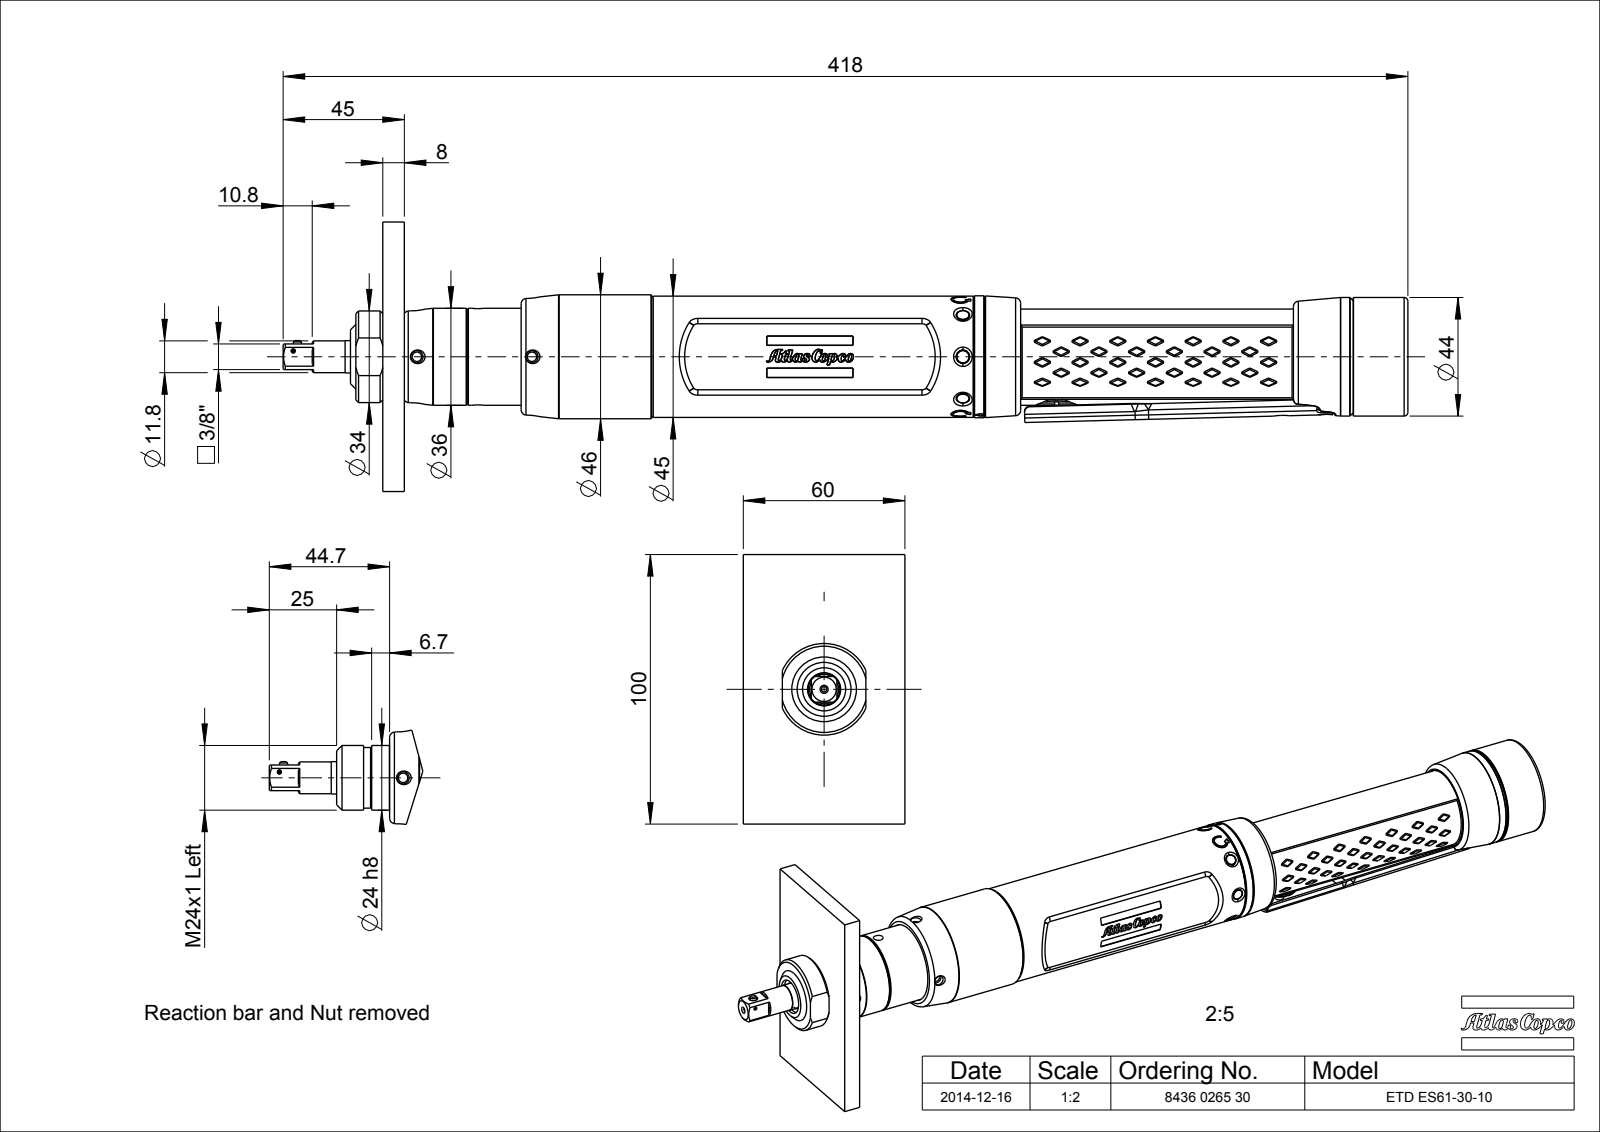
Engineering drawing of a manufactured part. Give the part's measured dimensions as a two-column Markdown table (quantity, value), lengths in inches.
| quantity | value |
| --- | --- |
| part name | 4220388170_AF0; 4220388112_AF0; 4220388172_AF0_ASM; 4220388180_ASM (+8 more) |
| STEP written by | PRO/ENGINEER BY PARAMETRIC TECHNOLOGY CORPORATION, 2013410 (CONFIG_CONTROL_DESIGN) |
| units | inches |
| bodies | 42 solids, 5159 faces (2029 planar, 893 cylindrical, 2237 other) |
| overall size | 16.44 × 3.937 × 2.362 |
| volume | 17.24 in³ |
| surface area | 359.5 in² |
| round holes (diameter × count) | 0.104 × 12, 0.129 × 12, 0.142 × 12, 0.165 × 6, 0.098 × 5, 0.197 × 5, 0.177 × 3, 0.63 × 2, 0.059 × 1, 0.079 × 1, 0.087 × 1, 0.102 × 1 |
| round bosses / shafts (diameter × count) | 0.087 × 9, 0.075 × 9, 0.062 × 9, 0.126 × 7, 0.115 × 3, 0.12 × 2, 0.1 × 2, 0.091 × 2 |
| partial cylindrical surfaces (radius × count) | 0.008 × 60, 0.016 × 33, 0.079 × 28, 0.039 × 18, 0.02 × 14, 0.004 × 12, 0.01 × 10, 0.009 × 6 |
| main face-to-face distances | 0.315, 0.059, 2.362, 0.039, 13.747, 14.062, 13.688, 14.003, 3.937, 1.567 |
| hole center spacings | 0.244, 0.374, 0.578, 0.773, 0.934, 0.231, 0.529, 0.571 |
